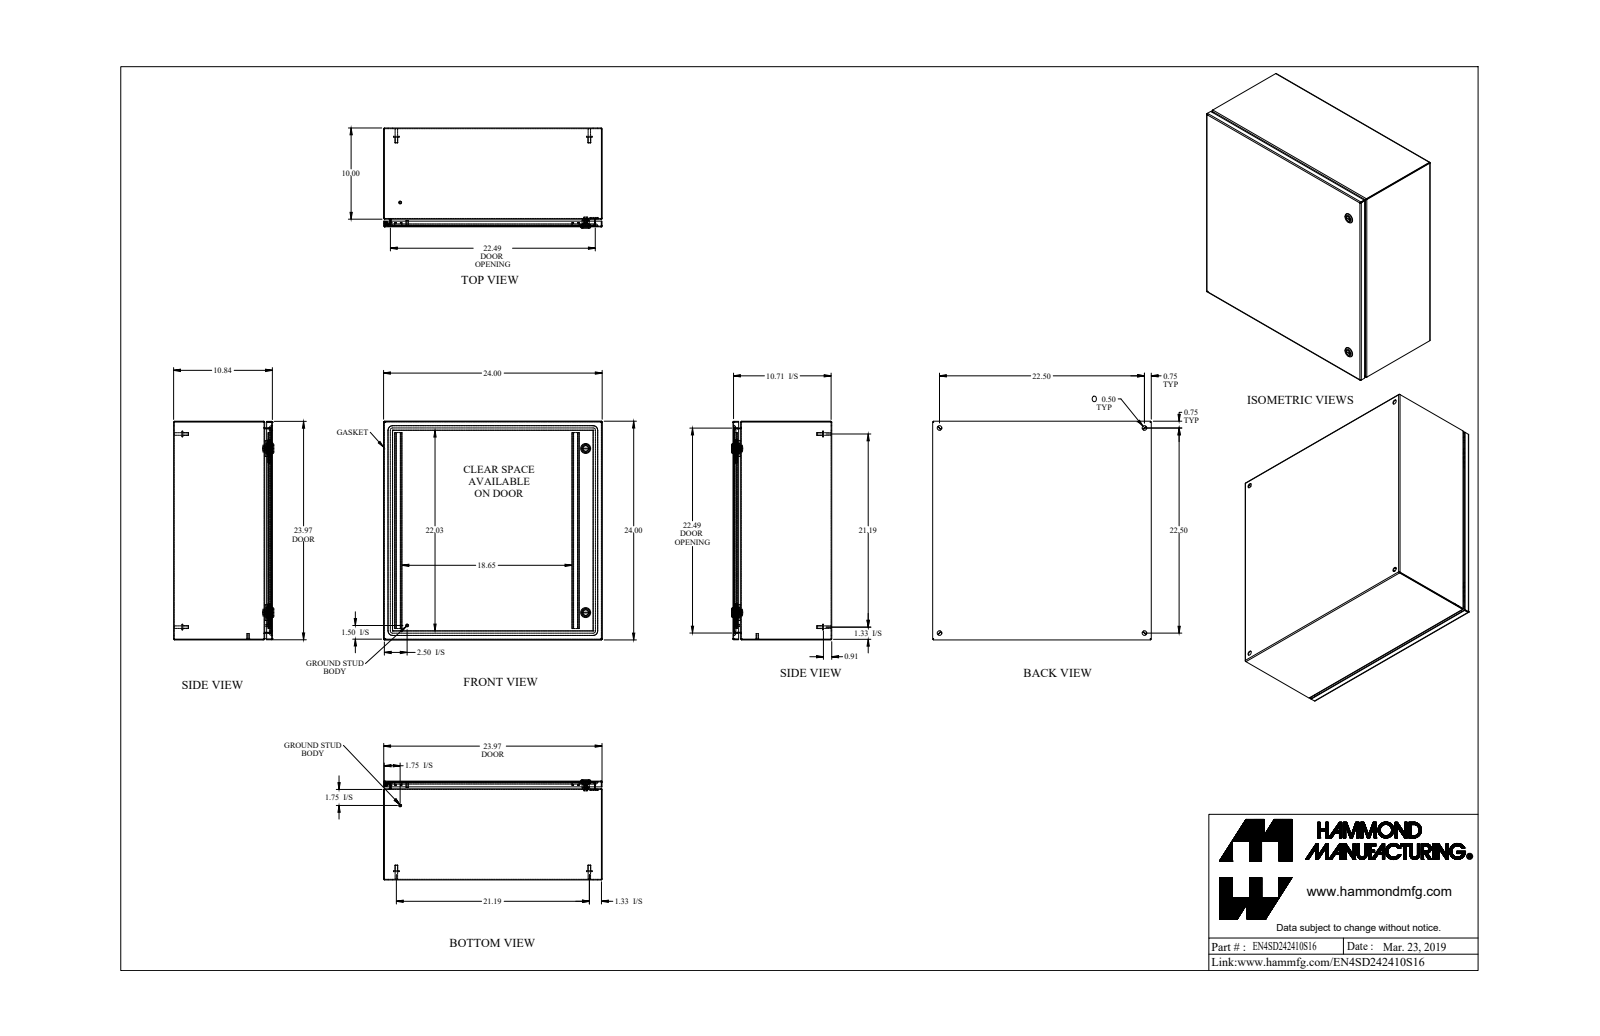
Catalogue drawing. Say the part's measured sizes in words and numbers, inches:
The part is named "EN4SD242410S16". Its 3-D file was written by "SolidWorks 2019 (AUTOMOTIVE_DESIGN)". It is 29 solids with 789 faces: 387 planar, 262 cylindrical and 140 other. Overall it measures 24 by 24 by 11.002 inches. Its volume is 177.7 cubic inches and its surface area 4 981 square inches. Round holes: 6 of diameter 0.5, 2 of diameter 0.197, 2 of diameter 0.387, 2 of diameter 0.63, 2 of diameter 0.768, 1 of diameter 0.172, 1 of diameter 0.24, 1 of diameter 0.242. Round bosses or shafts: 6 of diameter 0.625, 6 of diameter 0.313, 4 of diameter 0.275, 2 of diameter 1.1, 2 of diameter 0.785, 2 of diameter 0.525, 2 of diameter 0.25, 2 of diameter 0.236. Partial cylindrical surfaces (rounded edges, fillets, slot ends): 16 of radius 0.036, 16 of radius 0.108, 16 of radius 0.25, 12 of radius 0.01, 12 of radius 0.048, 8 of radius 0.1, 4 of radius 0.006, 4 of radius 0.062. The main face-to-face distances are 0.072, 10.77, 23.928, 10.698, 10.842, 23.856, 24, 0.842, 9.928, 0.75. The hole center spacings are 22.5, 2.488, 20.278, 21.557, 29.491, 31.82, 18.
